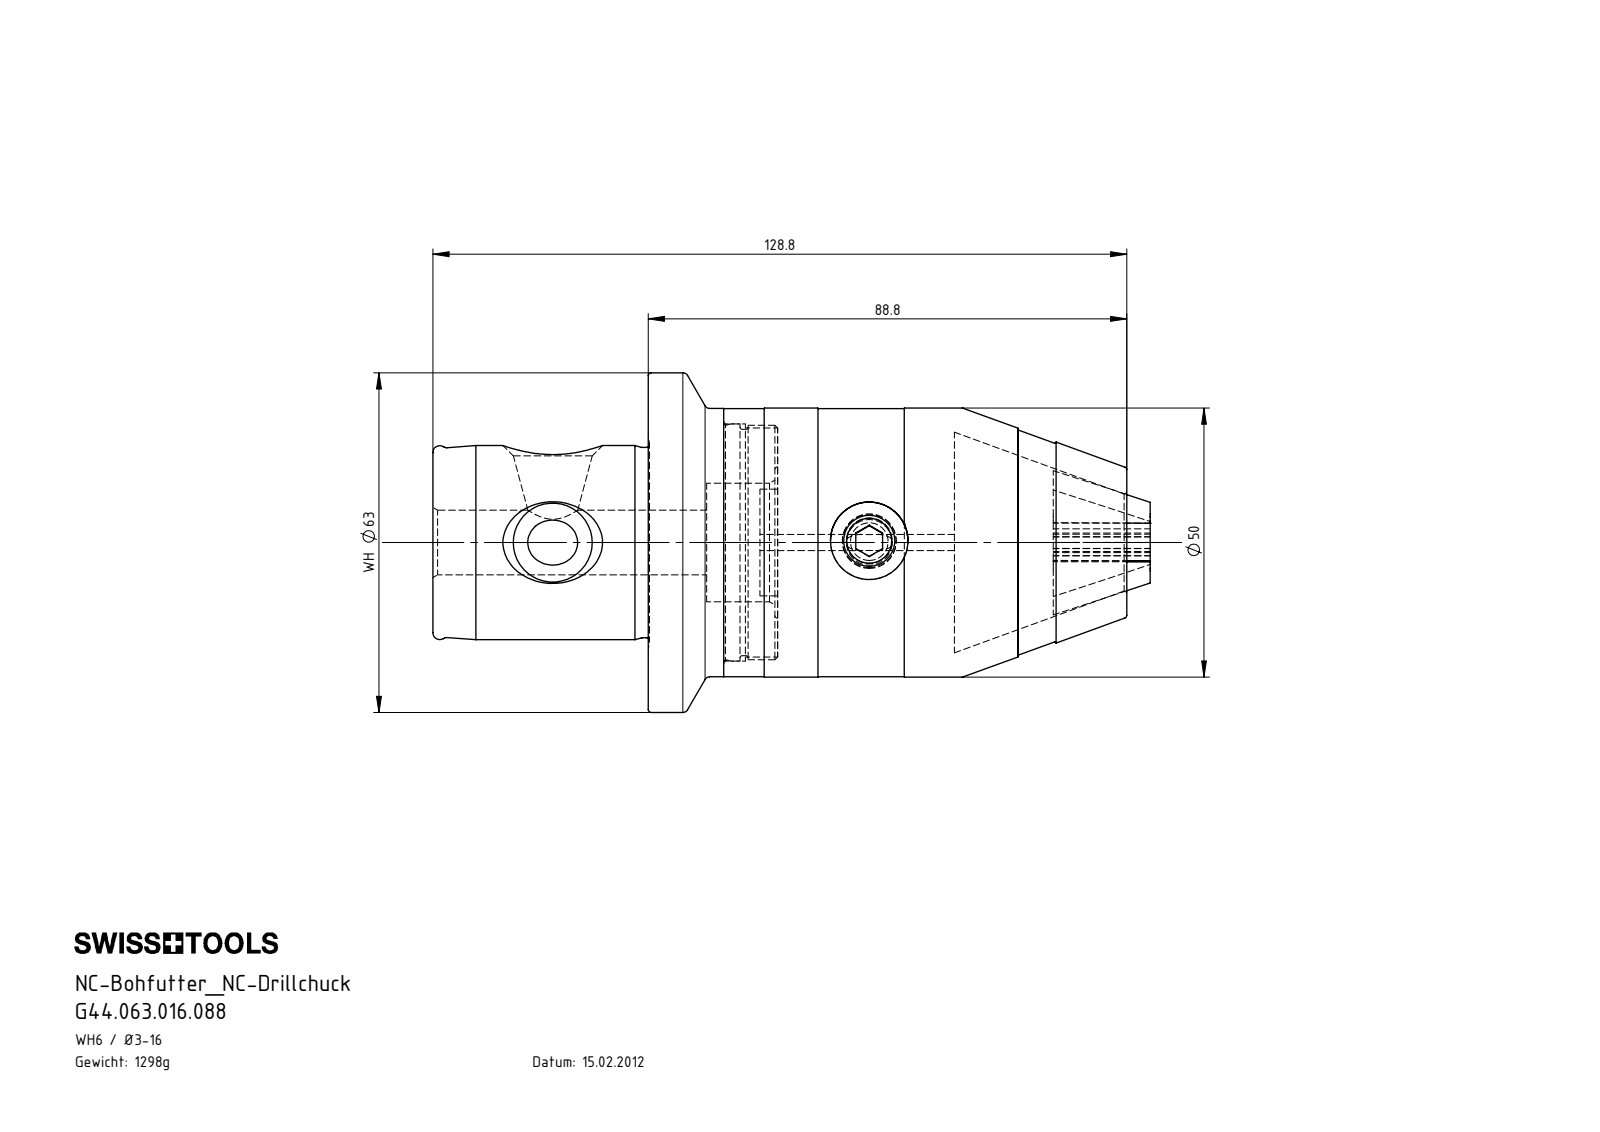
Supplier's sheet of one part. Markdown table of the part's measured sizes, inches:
| quantity | value |
| --- | --- |
| part name | Backe ø2.5-16; Bohrfutterø2.5-16_A; WH6.BF2.K01.088; WH6-BF2.K01.014 (+2 more) |
| STEP written by | SolidWorks 2022 (AUTOMOTIVE_DESIGN) |
| units | inches |
| bodies | 6 solids, 217 faces (57 planar, 57 cylindrical, 103 other) |
| overall size | 5.242 × 2.48 × 2.48 |
| volume | 10.25 in³ |
| surface area | 61.65 in² |
| round holes (diameter × count) | 0.118 × 1, 0.335 × 1, 0.472 × 1, 0.567 × 1, 0.866 × 1, 1.102 × 1, 1.673 × 1, 1.732 × 1 |
| round bosses / shafts (diameter × count) | 2.48 × 1, 1.966 × 1, 1.961 × 1, 1.958 × 1, 1.717 × 1, 1.713 × 1, 1.654 × 1, 1.417 × 1 |
| partial cylindrical surfaces (radius × count) | 0.012 × 6, 0.02 × 6 |
| main face-to-face distances | 2.236, 0.945, 1.291, 0.944, 1.293, 1.575, 2.519, 2.52, 3.811, 0.394 |
